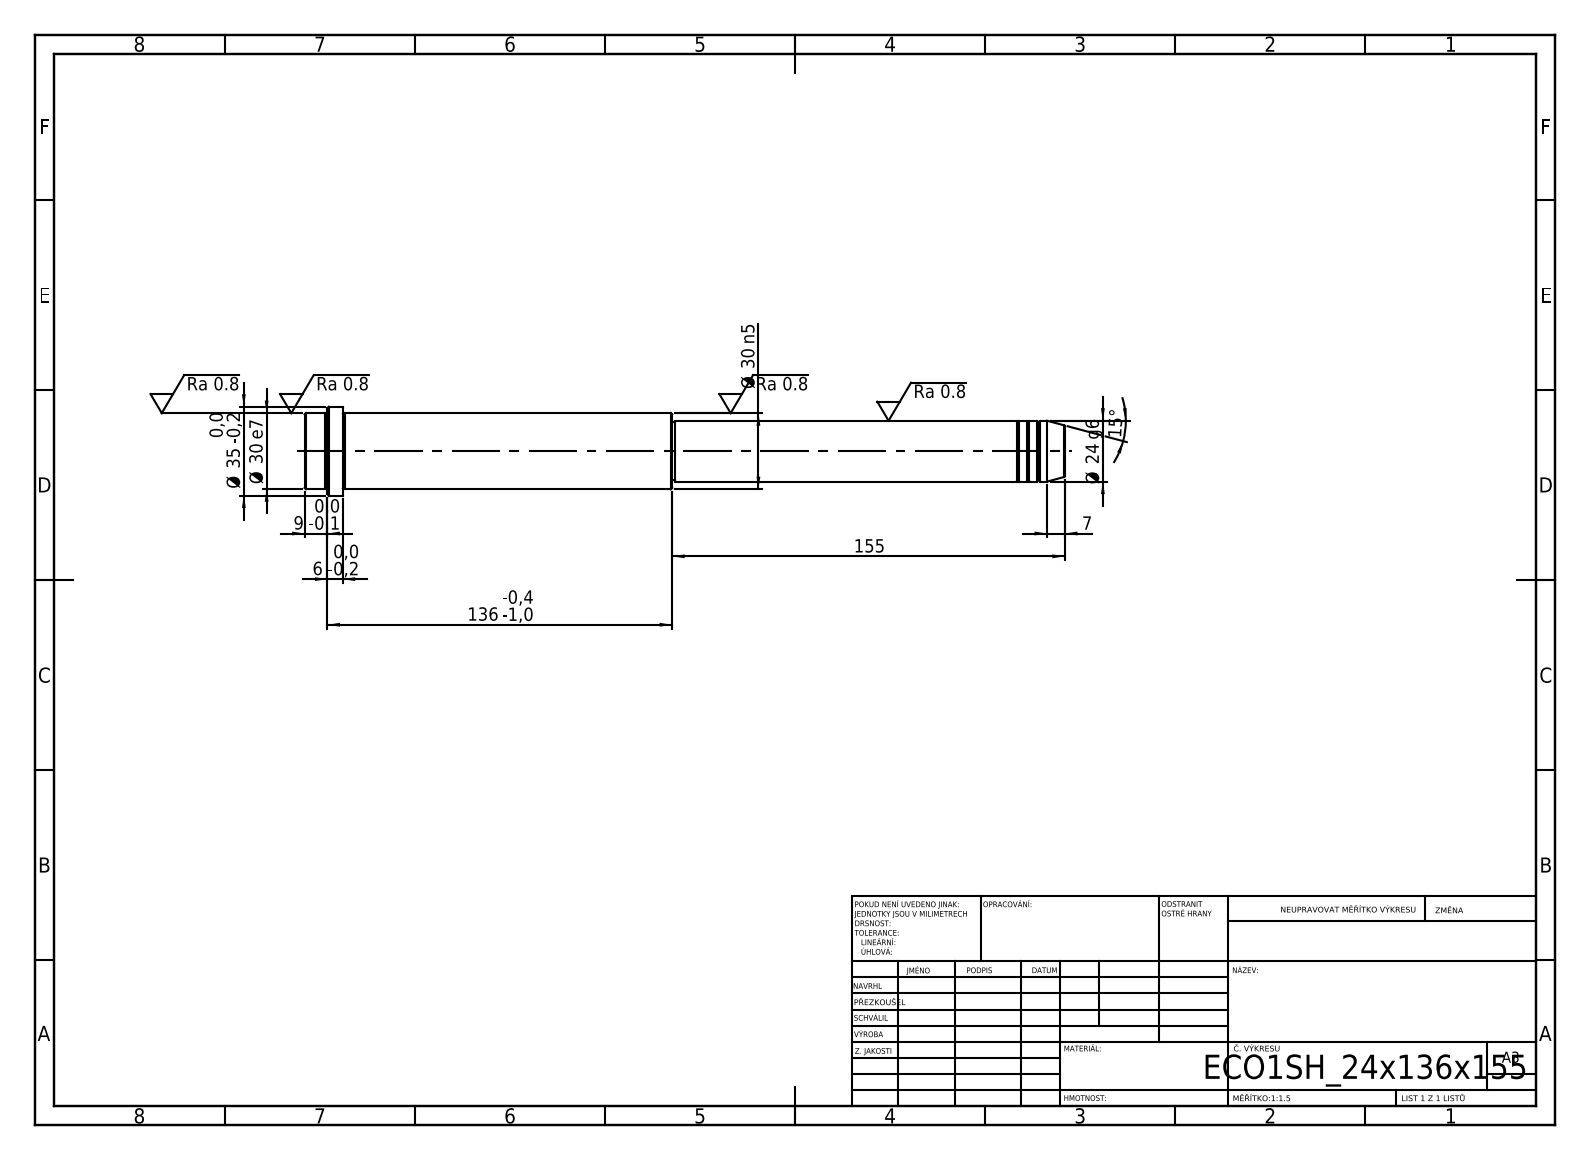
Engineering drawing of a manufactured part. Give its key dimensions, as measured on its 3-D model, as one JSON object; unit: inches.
{"step_written_by": "SolidWorks 2019 (CONFIG_CONTROL_DESIGN)", "units": "inches", "bodies": {"solids": 1, "faces": 52, "planar": 6, "cylindrical": 16, "other": 30}, "overall_size": [11.811, 1.378, 1.378], "volume_in3": 10.58, "surface_area_in2": 42.49, "round_bosses_or_shafts": [[1.378, 1], [1.181, 1], [0.945, 1], [0.906, 1]], "face_to_face_distances": [11.811, 11.22, 0.591, 6.102, 5.118, 5.709, 11.457, 5.354, 0.236, 0.354]}
